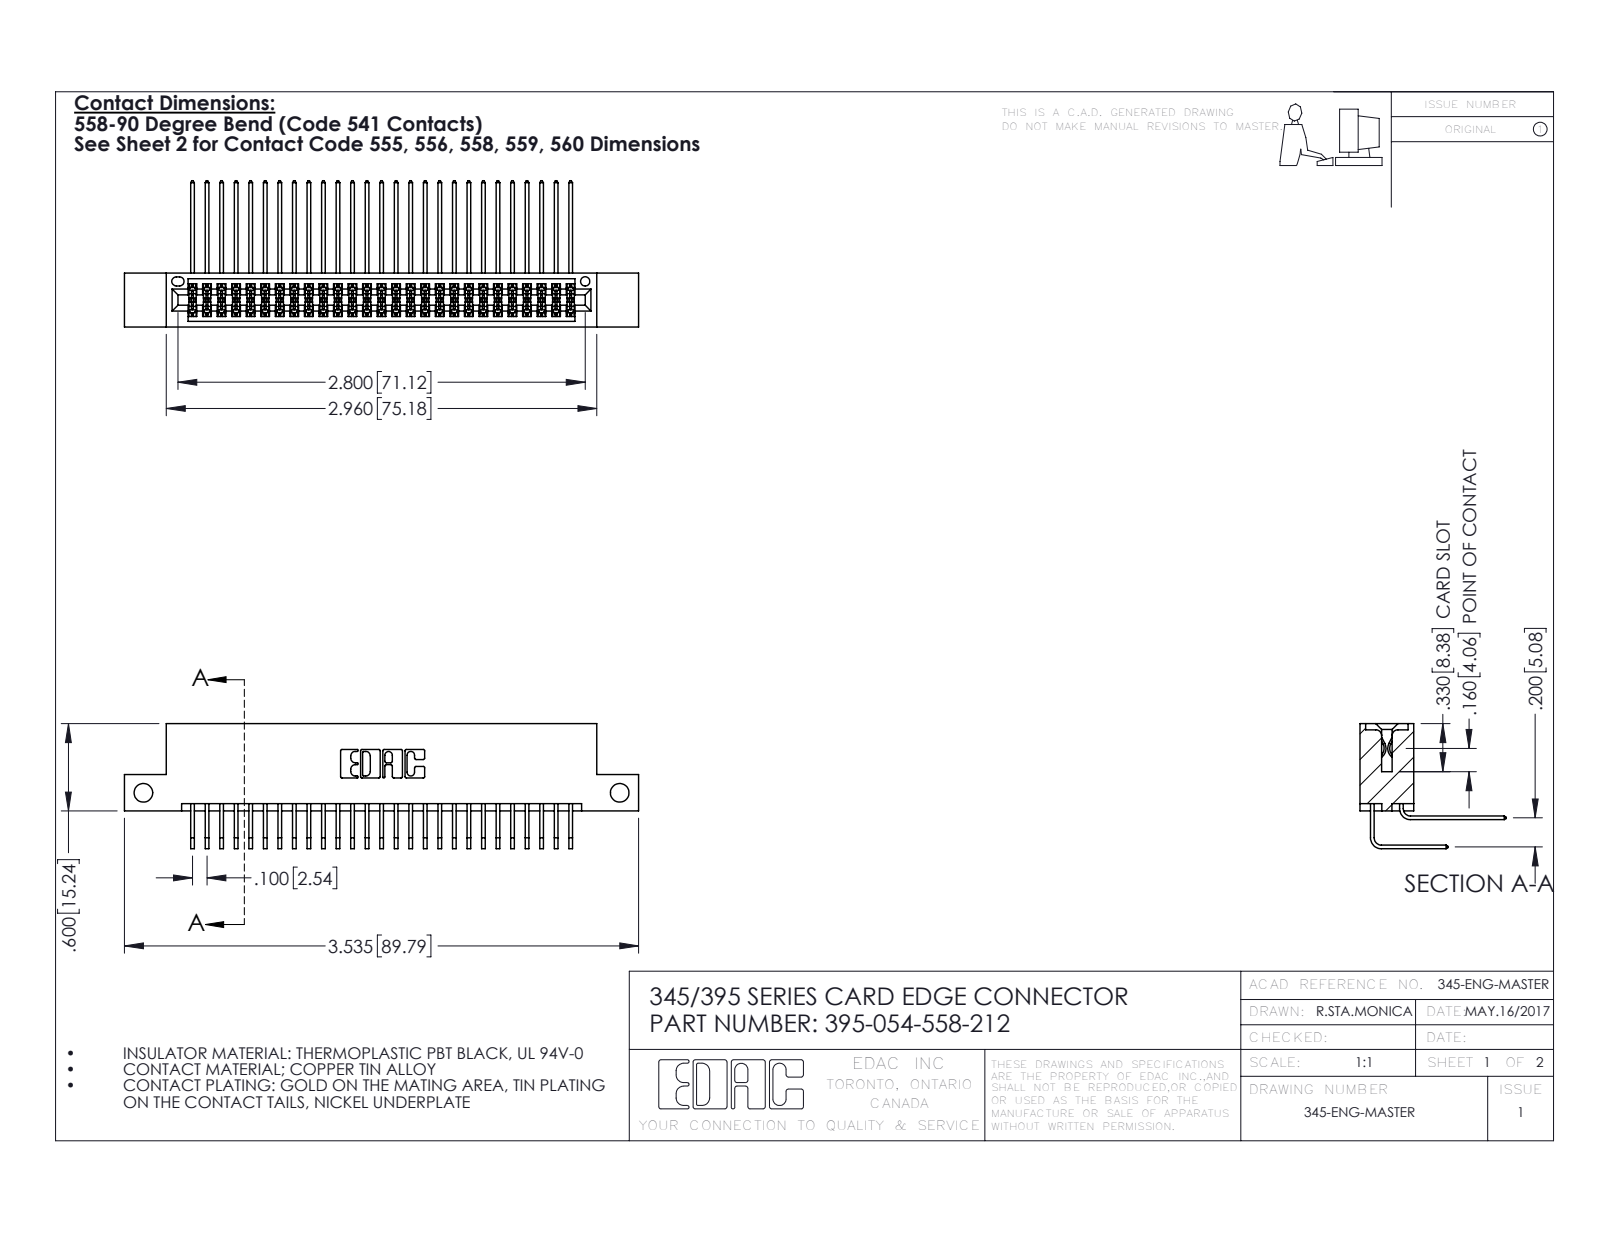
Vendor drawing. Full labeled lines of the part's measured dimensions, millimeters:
Part name (STEP PRODUCT): 345-292-001_558 Tail - 2; 345 Part_Flush Mounting Lugs - Side Mount; 395-054-558-212; 345-292-001_558 559 Tail - 1
STEP written by: SolidWorks 2016 (CONFIG_CONTROL_DESIGN)
Units: millimetres
Bodies: 55 solids, 2934 faces (1970 planar, 964 cylindrical, 0 other)
Overall size (bounding box): 89.8 × 25.5 × 21.8
Volume: 8 800 mm³ · Surface area: 14 060 mm²
Round holes (diameter × count): ⌀3.3 ×2, ⌀1.6 ×1
Partial cylindrical surfaces — rounded edges, fillets, slot ends (radius × count): R0.2 ×82, R0.3 ×22, R0.2 ×6, R0.8 ×6, R0.7 ×3, R0.4 ×2, R0.5 ×2, R0.6 ×2
Main face-to-face distances: 5.1, 1.8, 7.6, 9.4, 2.5, 6.9, 0.6, 5.7, 7.2, 0.6
Hole centre spacings: 83.2
